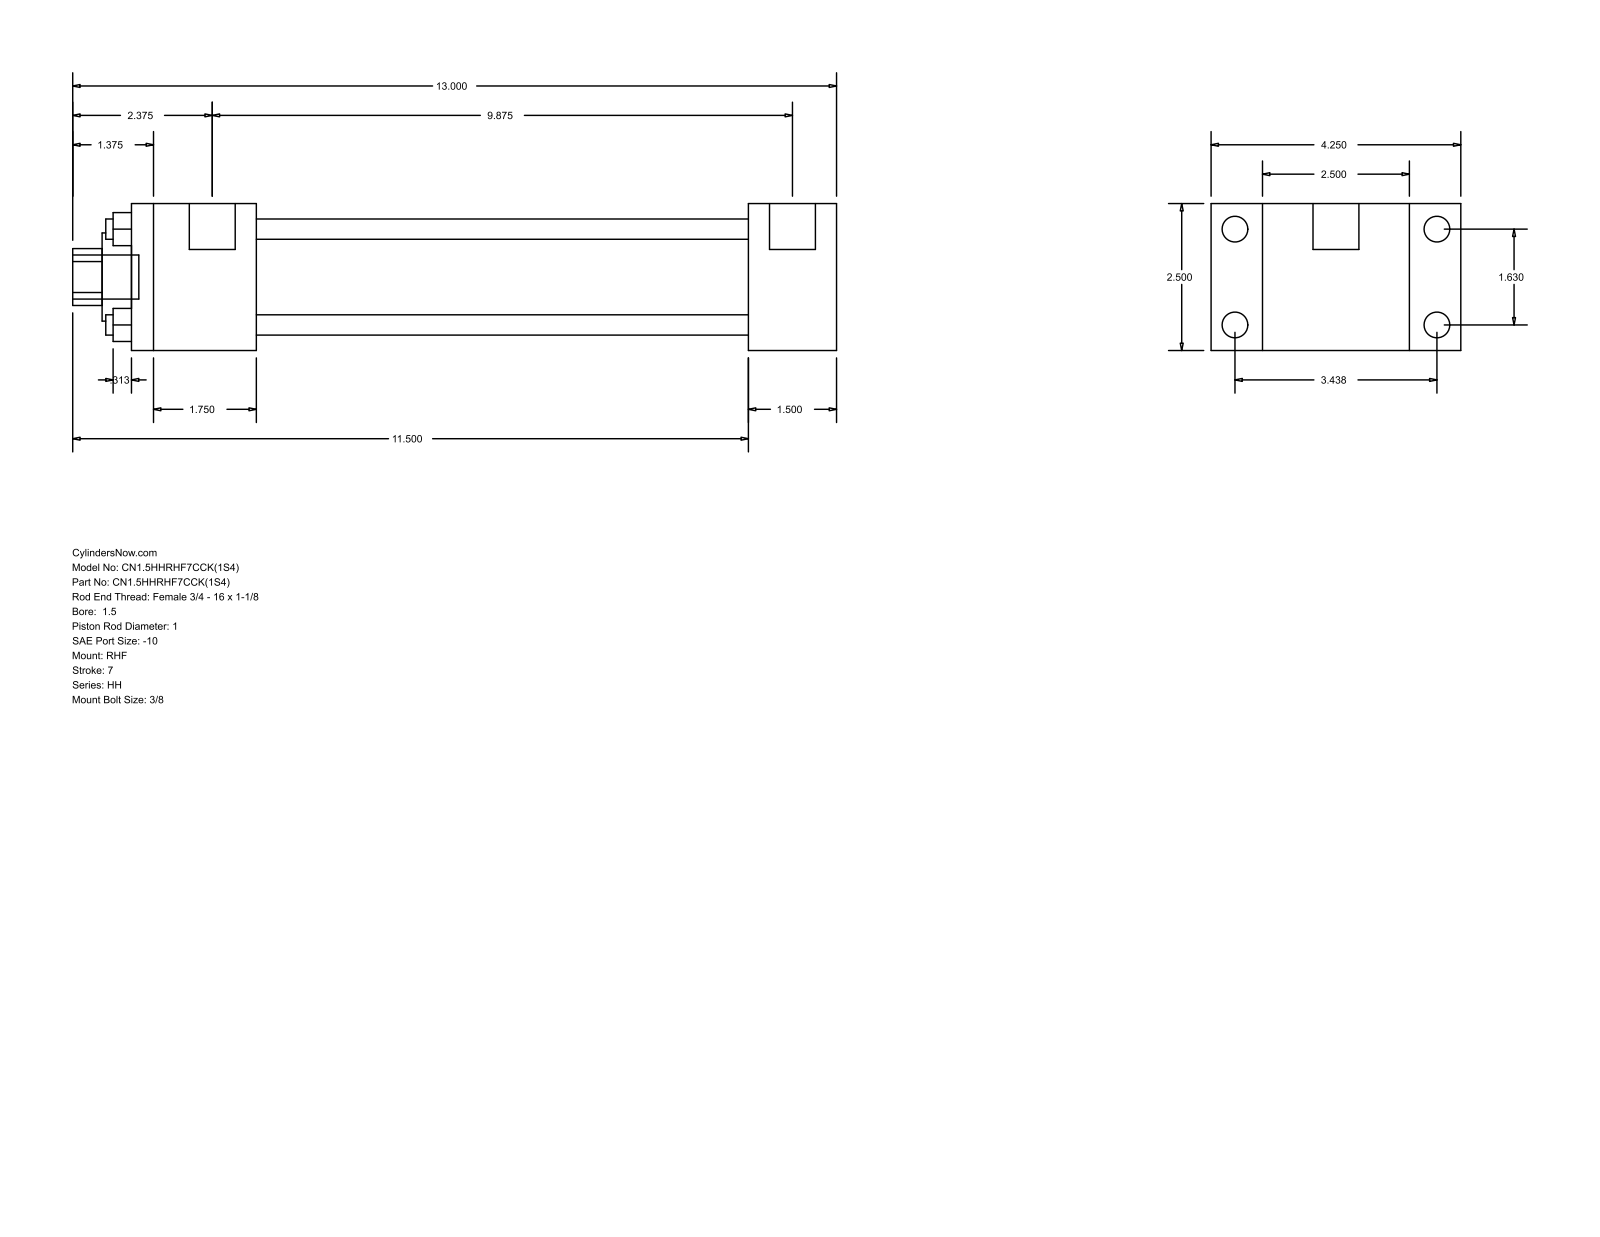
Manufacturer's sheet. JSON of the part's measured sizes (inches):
{"part_name": "HH_RHF__0150_1", "step_written_by": "GSSL Pune (CONFIG_CONTROL_DESIGN)", "units": "inches", "bodies": {"solids": 0, "faces": 88, "planar": 60, "cylindrical": 28, "other": 0}, "overall_size": [13, 4.25, 2.5], "round_holes": [[0.345, 4], [1, 1], [1.5, 1], [1.75, 1]], "round_bosses_or_shafts": [[0.438, 4], [0.219, 4], [0.781, 2], [0.75, 1]], "partial_cylinders_radius": [[0.484, 1]], "face_to_face_distances": [2.5, 0.875, 3.375, 1.5, 4.25, 8.375, 9.875, 2.125, 10.5, 12], "hole_center_spacings": [1.152, 1.63, 2.305]}
